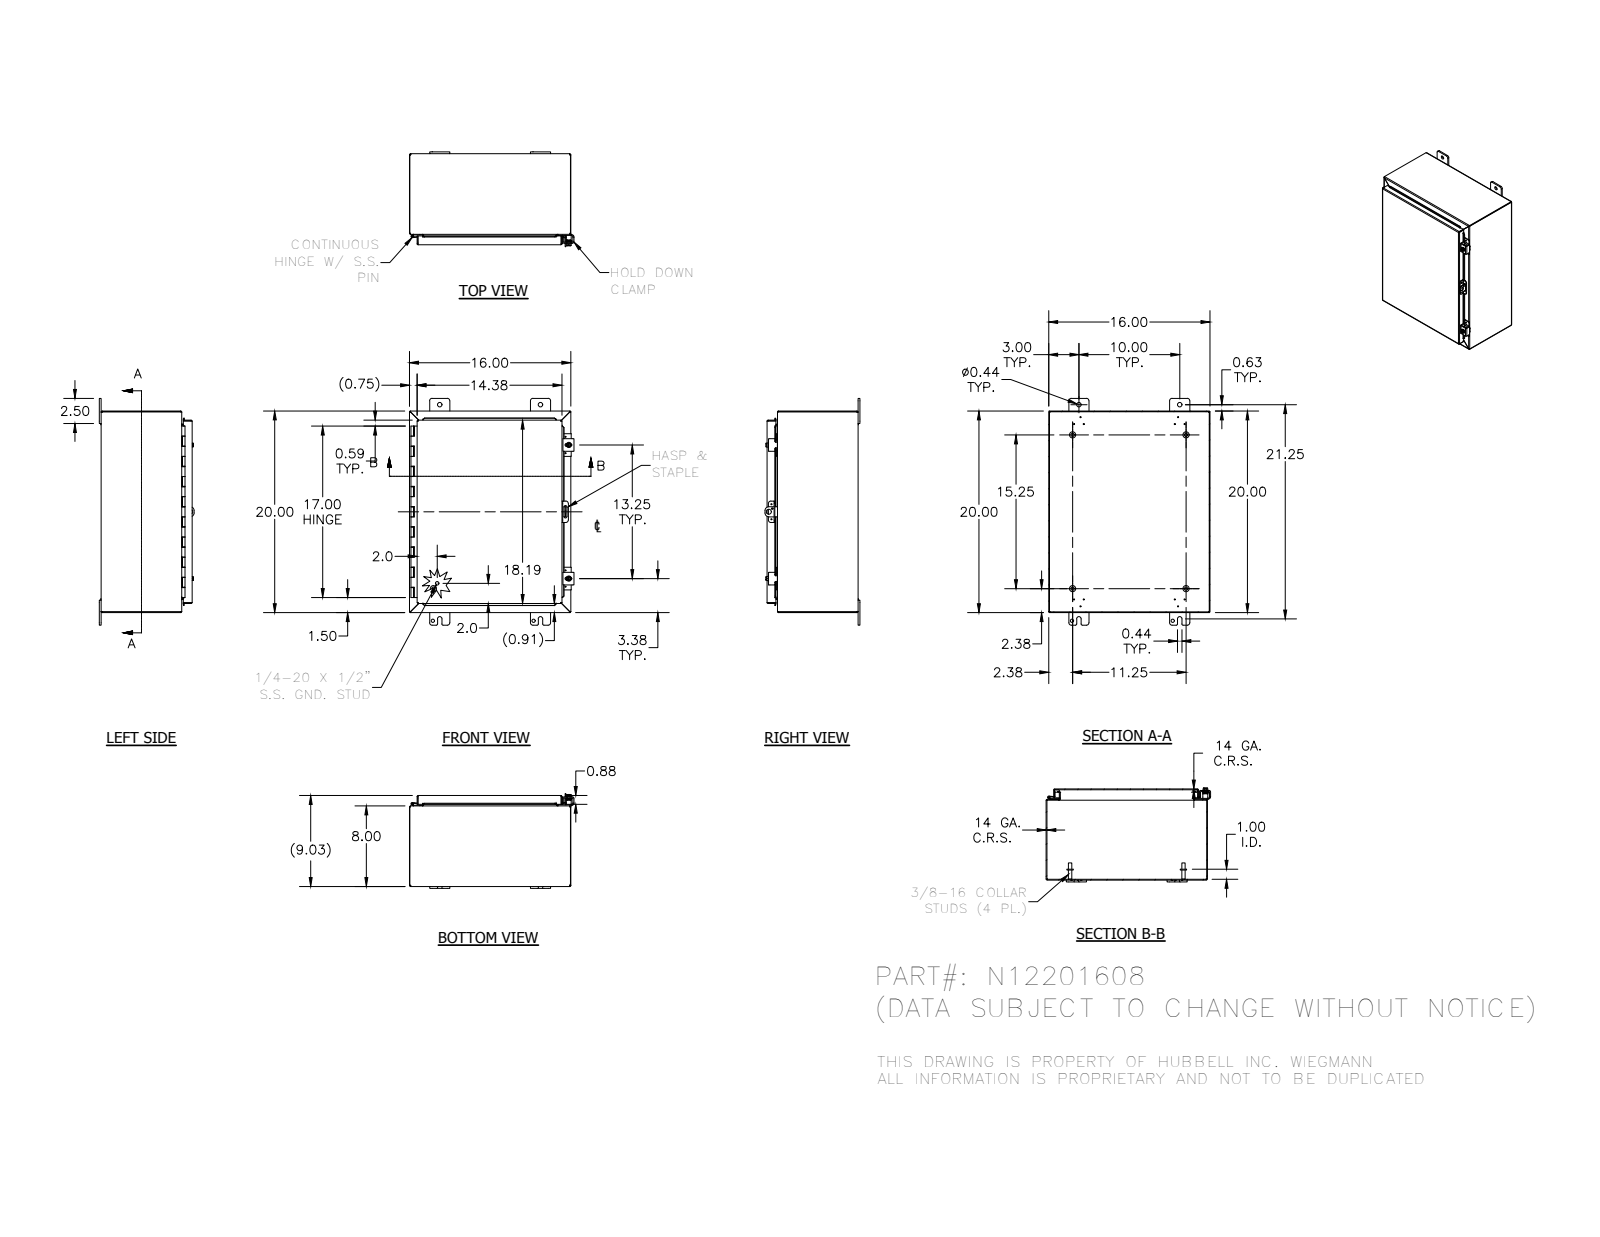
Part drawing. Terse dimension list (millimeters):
name: N12201608; 34840; 38420; N12201608BKP (+8 more)
written by: Autodesk Inventor 2012 (AUTOMOTIVE_DESIGN)
unit: mm
bodies: 27 solids, 948 faces (511 planar, 320 cylindrical, 117 other)
size: 571.5 × 414.3 × 239
volume: 1 873 000 mm³; area: 1 914 000 mm²
holes: 12× ⌀3, 7× ⌀2.8, 4× ⌀8, 4× ⌀11.1, 2× ⌀5.4, 2× ⌀7.1, 2× ⌀7.6, 1× ⌀3.2, 1× ⌀4, 1× ⌀12.7
bosses: 4× ⌀15.9, 4× ⌀8.4, 4× ⌀6.4, 2× ⌀13.2, 2× ⌀12.7, 2× ⌀8.9, 2× ⌀2.9, 1× ⌀8.6
rounds: 27× R0.8, 25× R1.6, 25× R3.2, 25× R6.4, 23× R0.8, 23× R2.7, 8× R1.8, 4× R2.5
face distances: 1.9, 227.6, 404.5, 225.7, 229.4, 506.1, 201.3, 26.2, 402.6, 406.4
hole spacings: 254, 19.3, 21.3, 23.9, 24.6, 40.5, 50.7, 238.3
